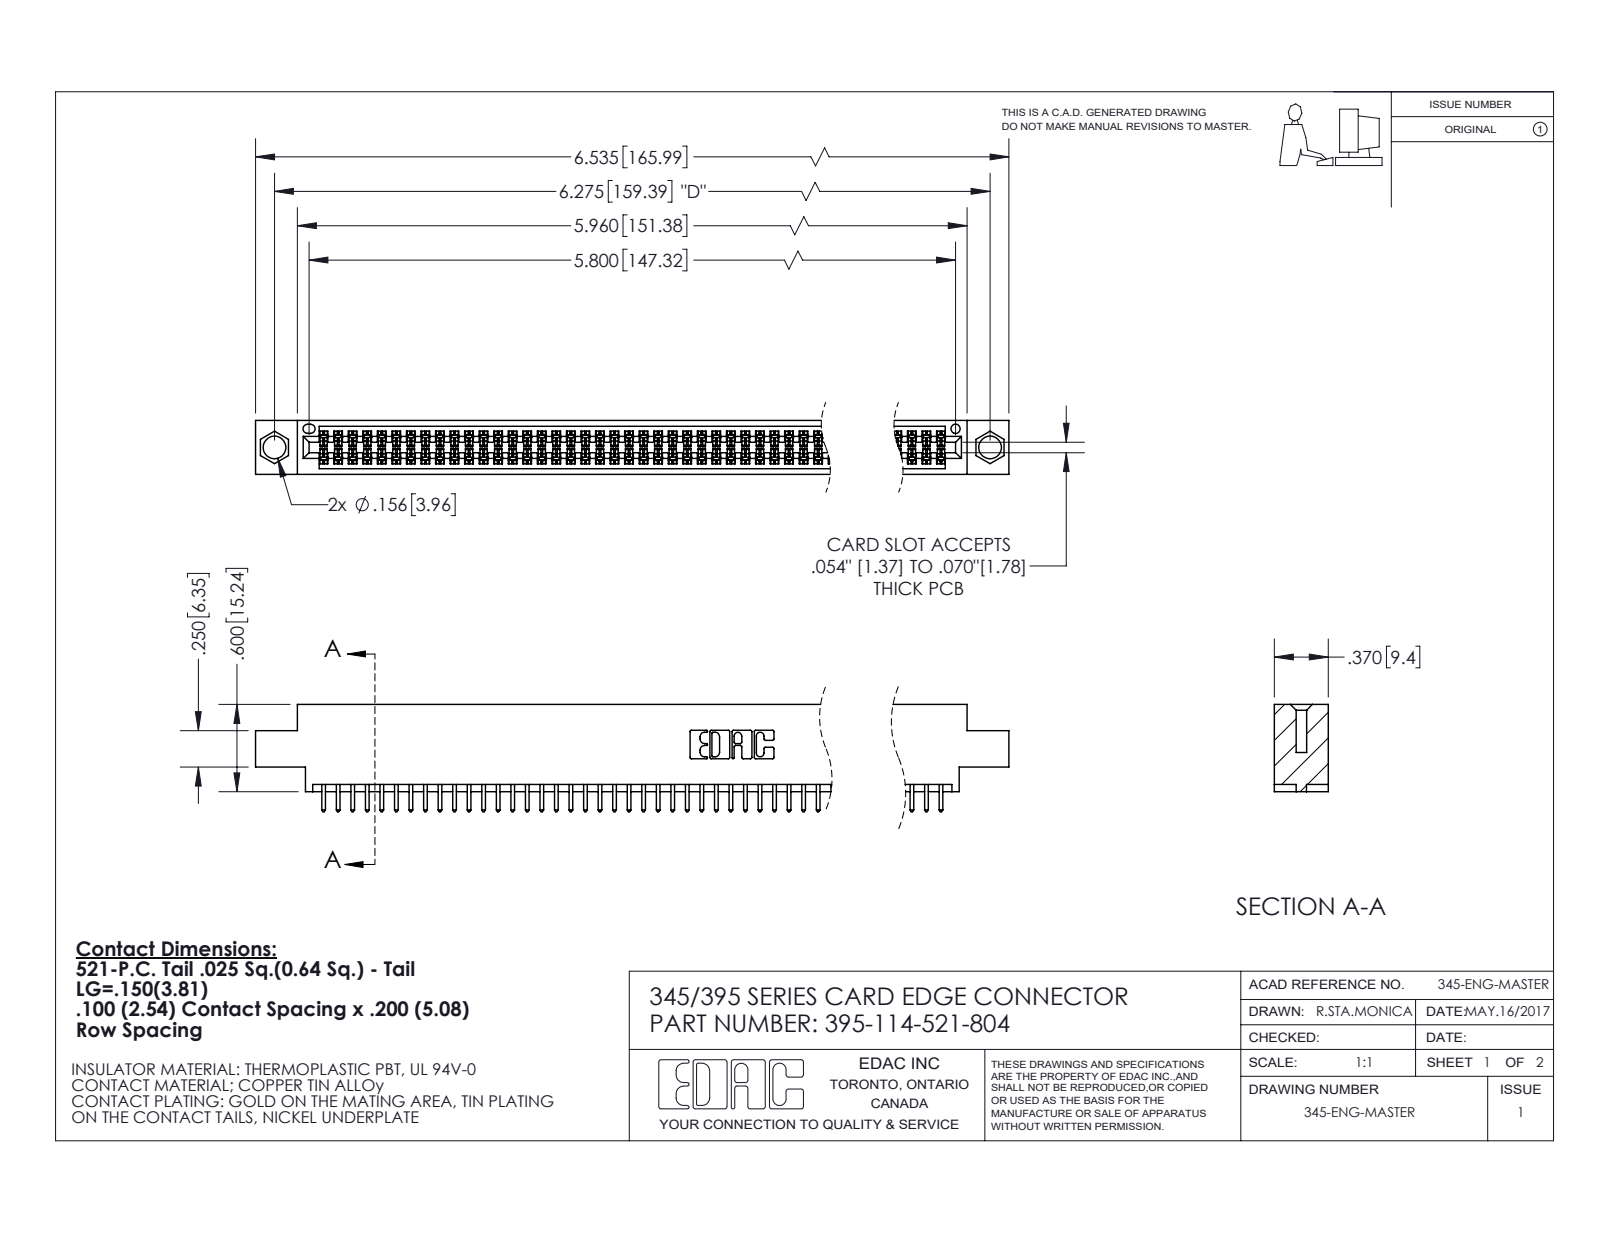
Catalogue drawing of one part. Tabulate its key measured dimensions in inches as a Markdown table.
| quantity | value |
| --- | --- |
| part name | 345-292-001_345-293-121; 395-114-521-804; 345 Part_0.170 Offset - 0.156 Dia-TI |
| STEP written by | SolidWorks 2020 (CONFIG_CONTROL_DESIGN) |
| units | inches |
| bodies | 115 solids, 5844 faces (3860 planar, 1984 cylindrical, 0 other) |
| overall size | 6.535 × 0.737 × 0.37 |
| volume | 0.976 in³ |
| surface area | 36.63 in² |
| round holes (diameter × count) | 0.156 × 2, 0.064 × 1 |
| partial cylindrical surfaces (radius × count) | 0.006 × 171, 0.01 × 114, 0.01 × 22, 0.007 × 6, 0.031 × 6, 0.026 × 3, 0.014 × 2, 0.019 × 2 |
| main face-to-face distances | 0.072, 0.298, 0.2, 0.37, 0.098, 0.272, 0.025, 0.225, 0.175, 0.149 |
| hole center spacings | 0.27, 6.039, 6.275 |
